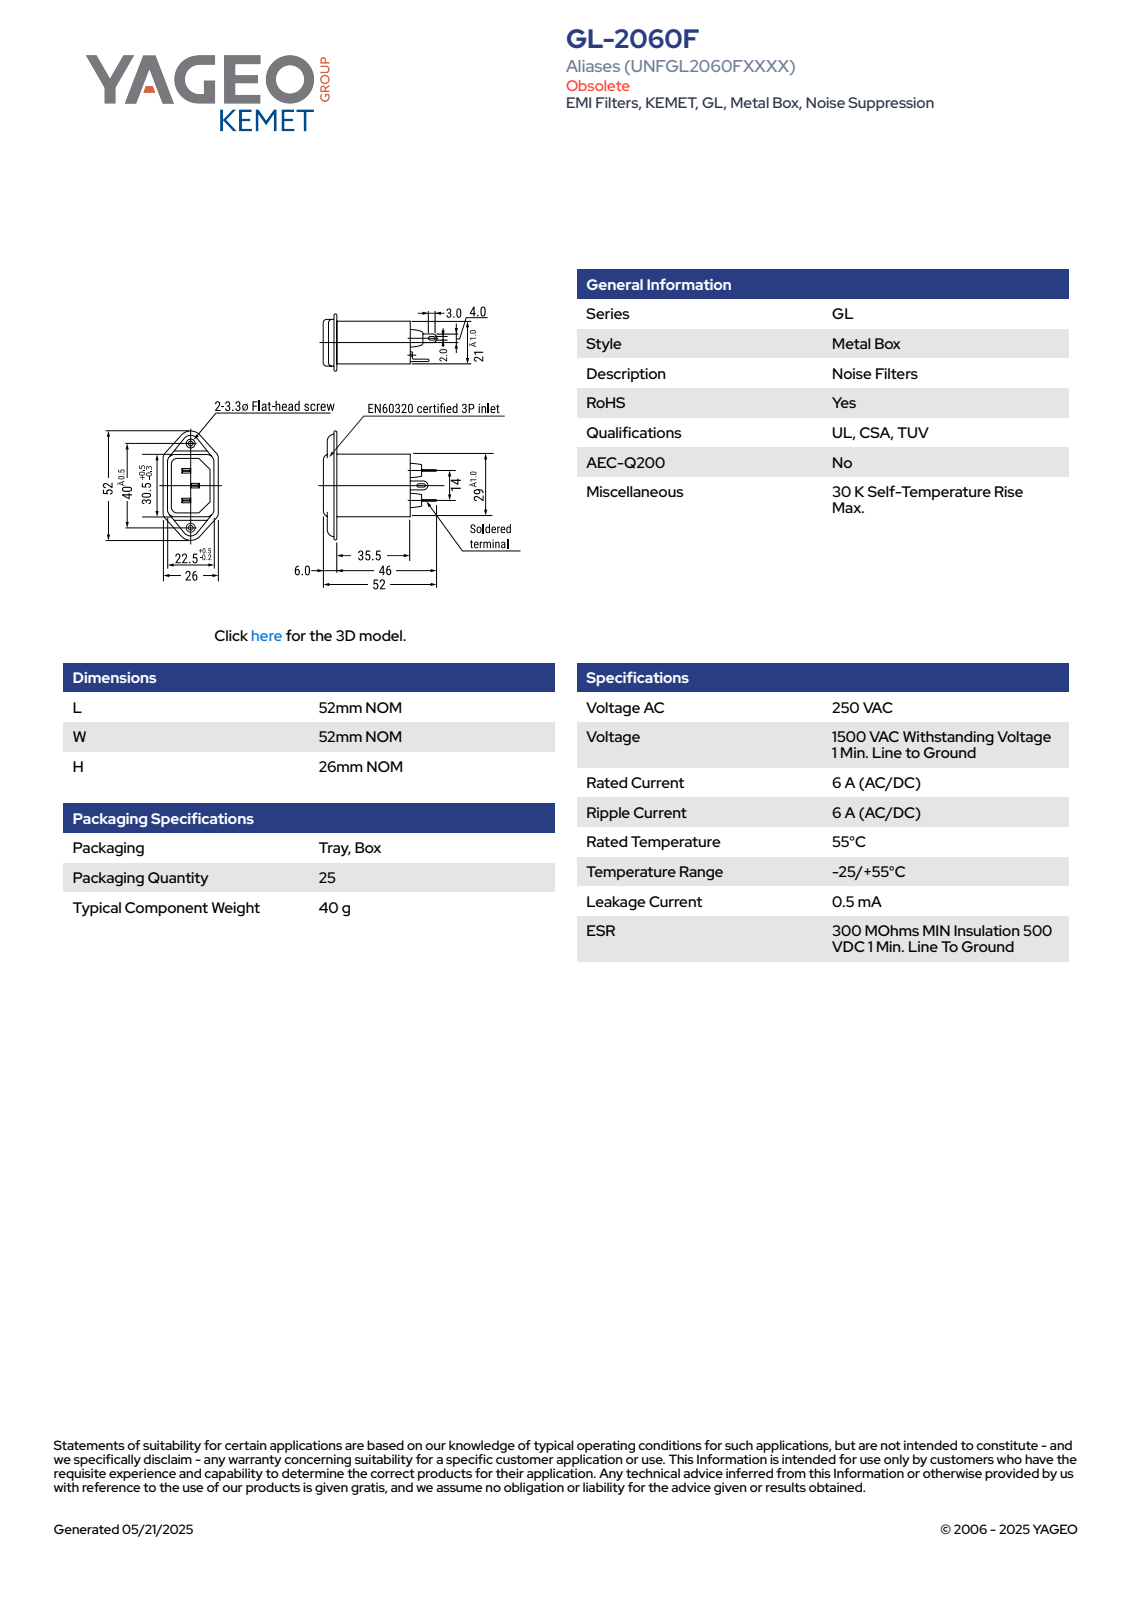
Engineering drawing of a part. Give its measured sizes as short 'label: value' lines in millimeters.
name: EC_KGLF_L52W52H26
written by: SolidWorks 2014 (AUTOMOTIVE_DESIGN)
unit: mm
bodies: 1 solid, 191 faces (114 planar, 61 cylindrical, 16 other)
size: 52 × 52 × 26
volume: 25 917 mm³; area: 7 076 mm²
holes: 2× ⌀3.3
bosses: 2× ⌀6
rounds: 24× R1, 13× R2, 2× R0.5, 2× R3, 1× R2.16
face distances: 22, 29, 2, 37.5, 35.5, 1, 0.5, 4, 21, 41.5
hole spacings: 40.5
